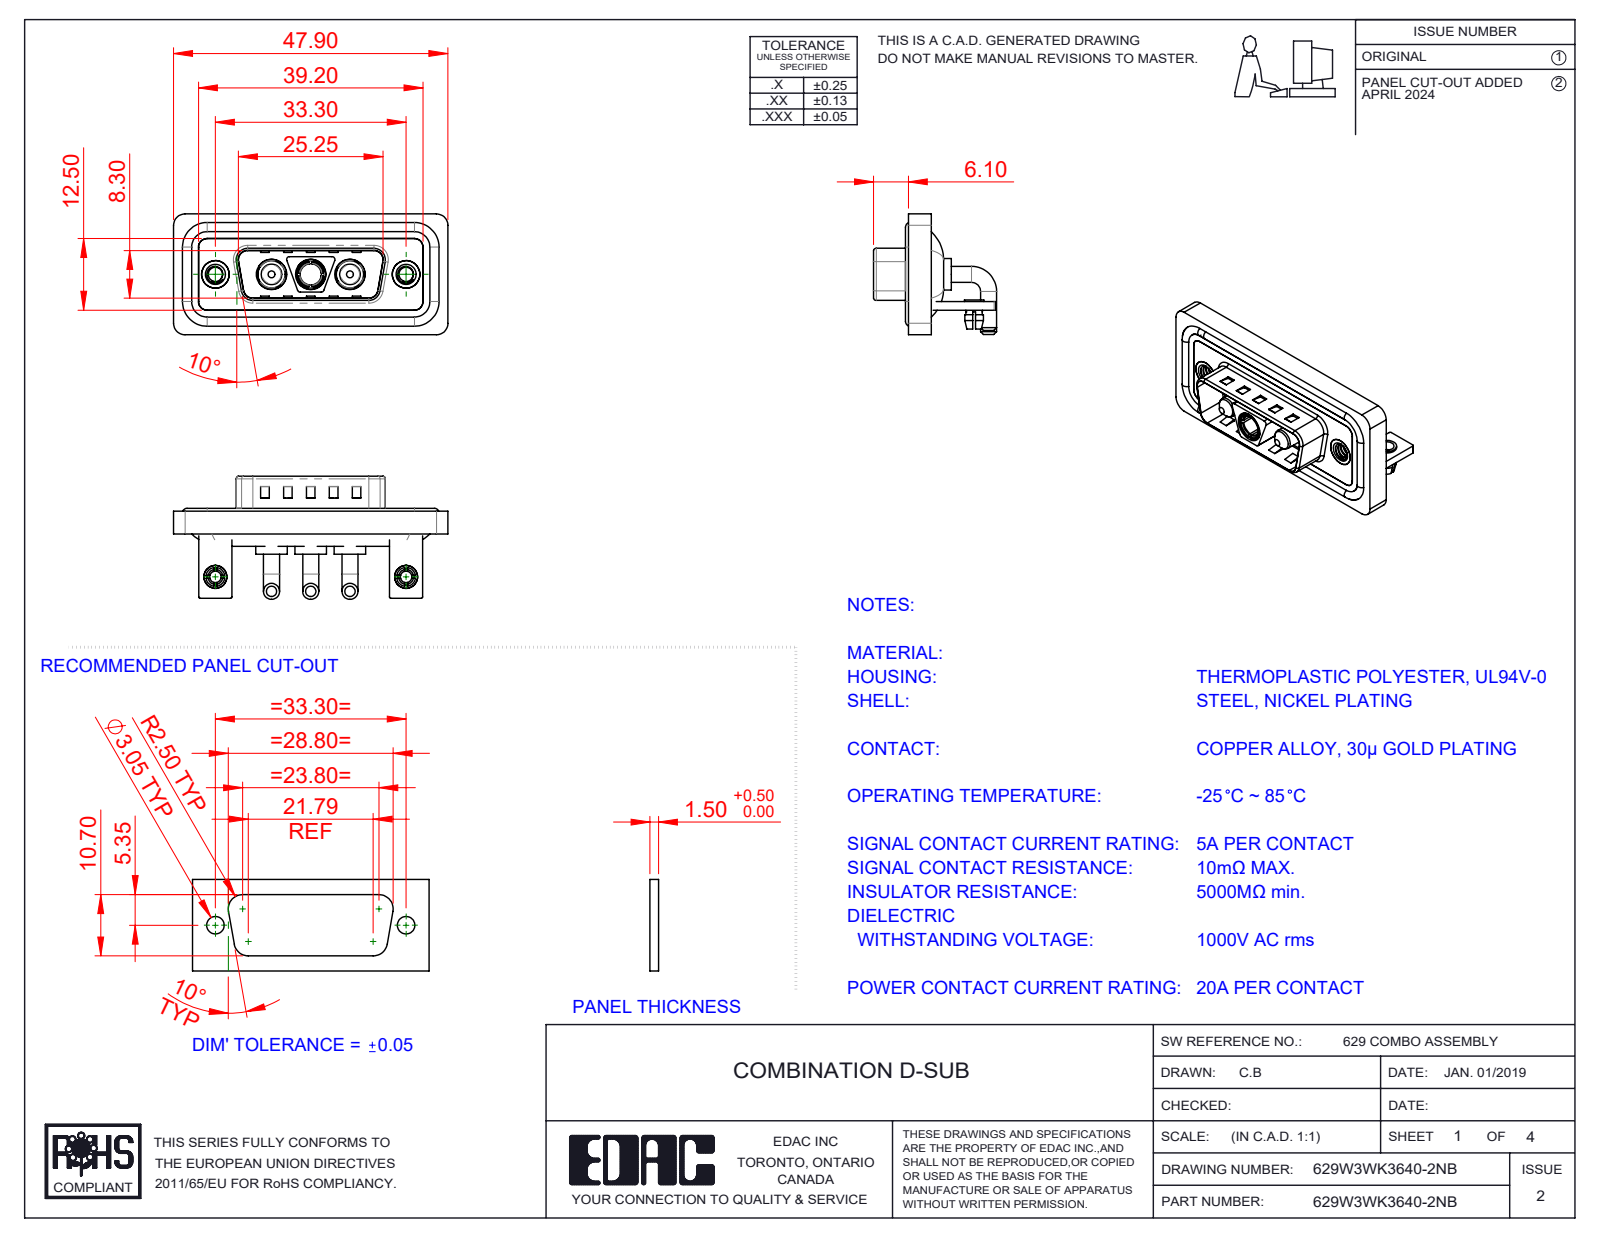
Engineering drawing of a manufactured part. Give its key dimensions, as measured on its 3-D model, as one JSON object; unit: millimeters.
{"part_name": "Power Socket_20A RA; 629Combo Waterproof Housing_15 Contacts; 629Combo Stabilizer Bracket; 629W3WK3640-2NB (+6 more)", "step_written_by": "SolidWorks 2023 (CONFIG_CONTROL_DESIGN)", "units": "millimeters", "bodies": {"solids": 17, "faces": 751, "planar": 299, "cylindrical": 306, "other": 146}, "overall_size": [47.9, 21.5, 21.1], "volume_mm3": 6193, "surface_area_mm2": 10214, "round_holes": [[2.5, 4], [4.85, 3], [5.3, 3], [2, 2], [3.2, 2], [4, 2], [4.8, 2], [5, 2], [3.7, 1]], "round_bosses_or_shafts": [[2.8, 6], [1.6, 4], [5.5, 3], [5.2, 3], [4.75, 3], [3.75, 3], [4.9, 2], [4, 2]], "partial_cylinders_radius": [[2, 21], [1.5, 18], [0.25, 16], [0.5, 13], [1.6, 8], [0.6, 4], [0.65, 4], [0.9, 4]], "face_to_face_distances": [0.4, 1.5, 0.8, 2.9, 1.1, 2.1, 3.7, 1.6, 1.2, 4.5], "hole_center_spacings": [6.85, 9.8, 16.65, 23.5, 33.3, 13.7]}
